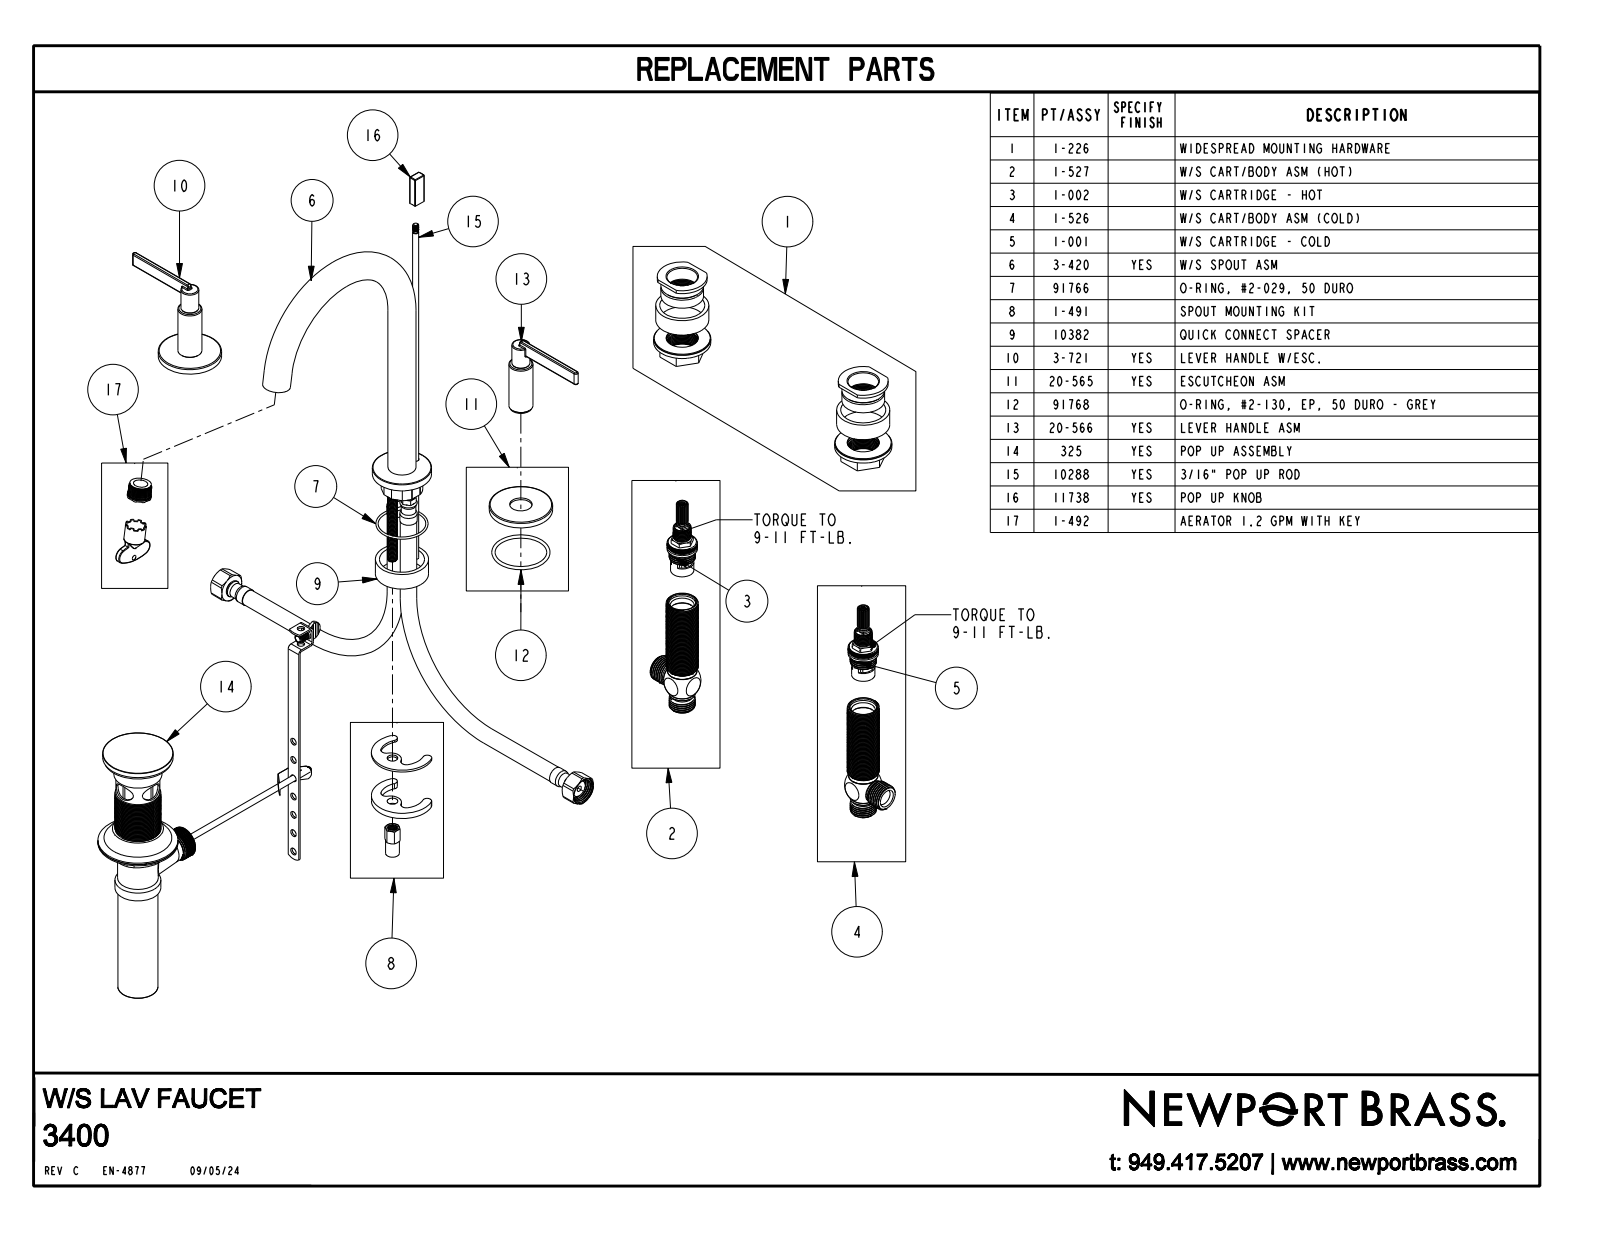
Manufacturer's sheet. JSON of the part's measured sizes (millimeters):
{"part_name": "3400", "step_written_by": "CREO PARAMETRIC BY PTC INC, 2019352 (CONFIG_CONTROL_DESIGN)", "units": "millimeters", "bodies": {"solids": 4, "faces": 136, "planar": 30, "cylindrical": 62, "other": 44}, "overall_size": [330.2, 239.9, 176.9], "volume_mm3": 211700, "surface_area_mm2": 51730, "round_holes": [[18.5, 1]], "round_bosses_or_shafts": [[50.3, 2], [22.2, 2], [19.1, 2], [18.5, 2], [14.3, 2], [13, 2], [47, 1]], "partial_cylinders_radius": [[0.8, 16], [0.5, 6], [1.5, 2], [1.9, 2], [11.9, 1], [22.3, 1]], "face_to_face_distances": [5.1, 6.4, 1.3, 3.8, 6.6, 1.5, 68.6, 63.5, 62.3, 62]}
